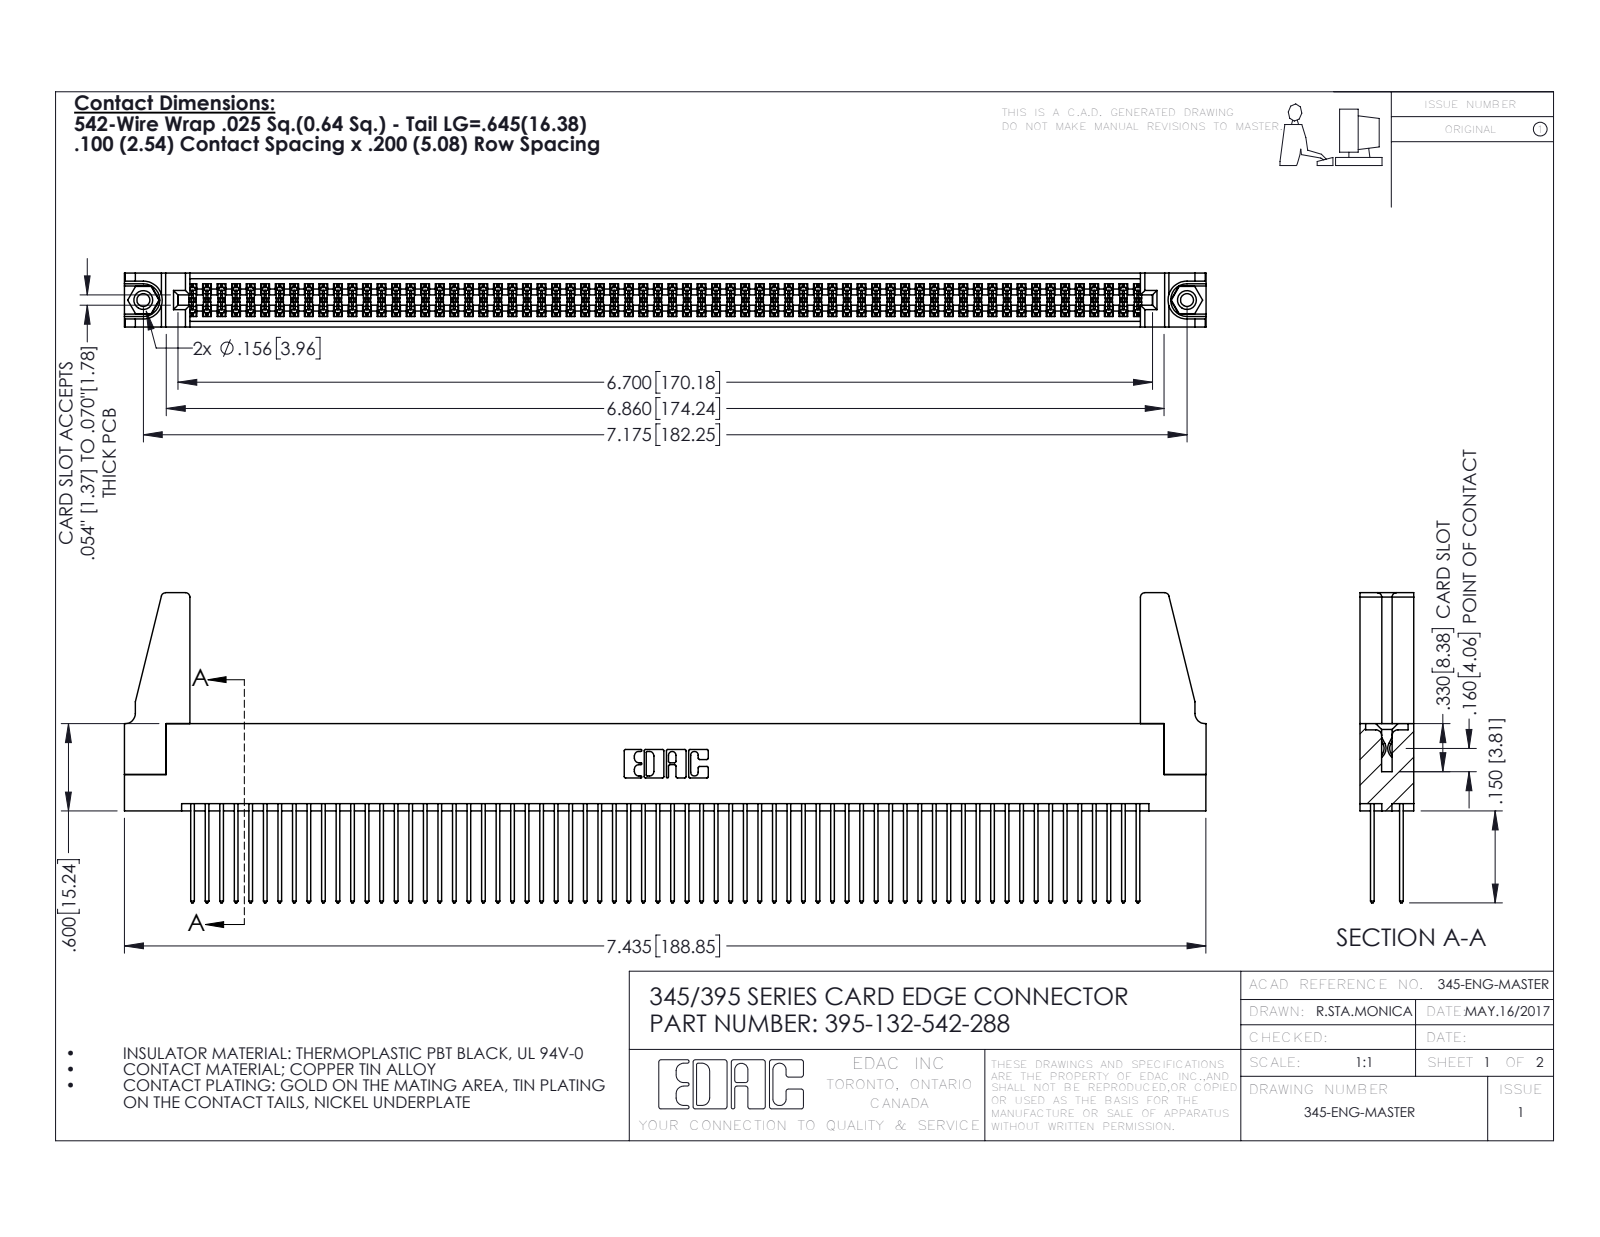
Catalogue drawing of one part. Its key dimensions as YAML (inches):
part_name: "345-250-001_345-250-001-102; 345 Part_Flush Mounting Lugs - 0.156 Dia-TH; 345-292-001_345-293-142; 395-132-542-288 (+1 more)"
step_written_by: "SolidWorks 2016 (CONFIG_CONTROL_DESIGN)"
units: inches
bodies: {solids: 137, faces: 6850, planar: 4508, cylindrical: 2326, other: 16}
overall_size: [7.436, 2.132, 0.37]
volume: 1.369
surface_area: 53.97
round_holes:
  - {diameter: 0.089, count: 2}
  - {diameter: 0.125, count: 2}
  - {diameter: 0.156, count: 2}
  - {diameter: 0.064, count: 1}
round_bosses_or_shafts:
  - {diameter: 0.155, count: 2}
partial_cylinders:
  - {radius: 0.006, count: 198}
  - {radius: 0.01, count: 132}
  - {radius: 0.01, count: 22}
  - {radius: 0.03, count: 8}
  - {radius: 0.007, count: 6}
  - {radius: 0.031, count: 6}
  - {radius: 0.026, count: 3}
  - {radius: 0.014, count: 2}
face_to_face_distances: [0.072, 0.298, 0.2, 0.098, 0.272, 0.025, 0.37, 0.225, 0.175, 0.149]
hole_center_spacings: [0.27, 6.939, 7.175]
